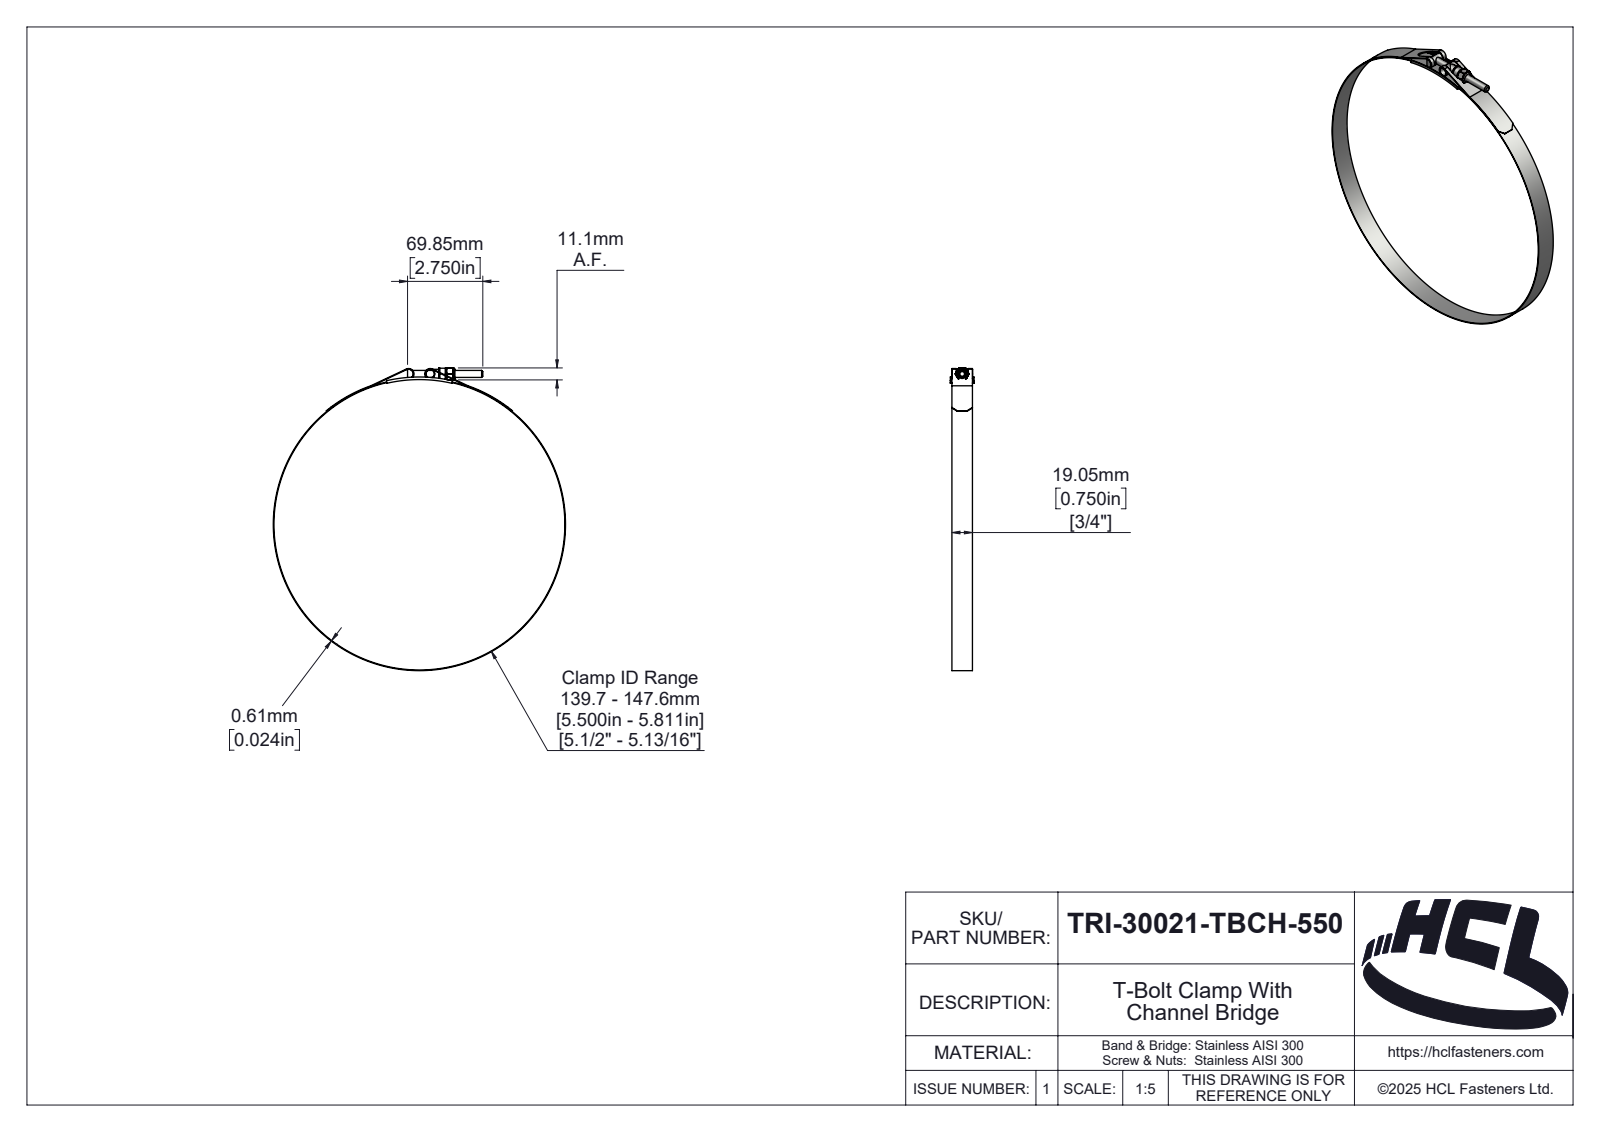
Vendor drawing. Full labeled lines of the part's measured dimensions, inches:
Part name (STEP PRODUCT): TRI-30021-TBCH-550
STEP written by: SolidWorks 2025 (AUTOMOTIVE_DESIGN)
Units: inches
Bodies: 6 solids, 330 faces (46 planar, 122 cylindrical, 162 other)
Overall size (bounding box): 11.062 × 10.678 × 0.866
Volume: 1.017 in³ · Surface area: 72.46 in²
Round holes (diameter × count): ⌀0.213 ×1, ⌀0.25 ×1, ⌀0.256 ×1, ⌀0.298 ×1, ⌀10.63 ×1
Round bosses / shafts (diameter × count): ⌀0.338 ×2, ⌀10.678 ×1, ⌀0.417 ×1
Partial cylindrical surfaces — rounded edges, fillets, slot ends (radius × count): R0.015 ×6, R0.02 ×2, R0.173 ×2, R0.197 ×2, R0.023 ×1, R0.095 ×1, R0.119 ×1, R0.126 ×1
Main face-to-face distances: 0.024, 0.75, 0.058, 0.808, 0.842, 0.034, 0.784, 0.029, 0.866, 0.818
Hole centre spacings: 5.512
